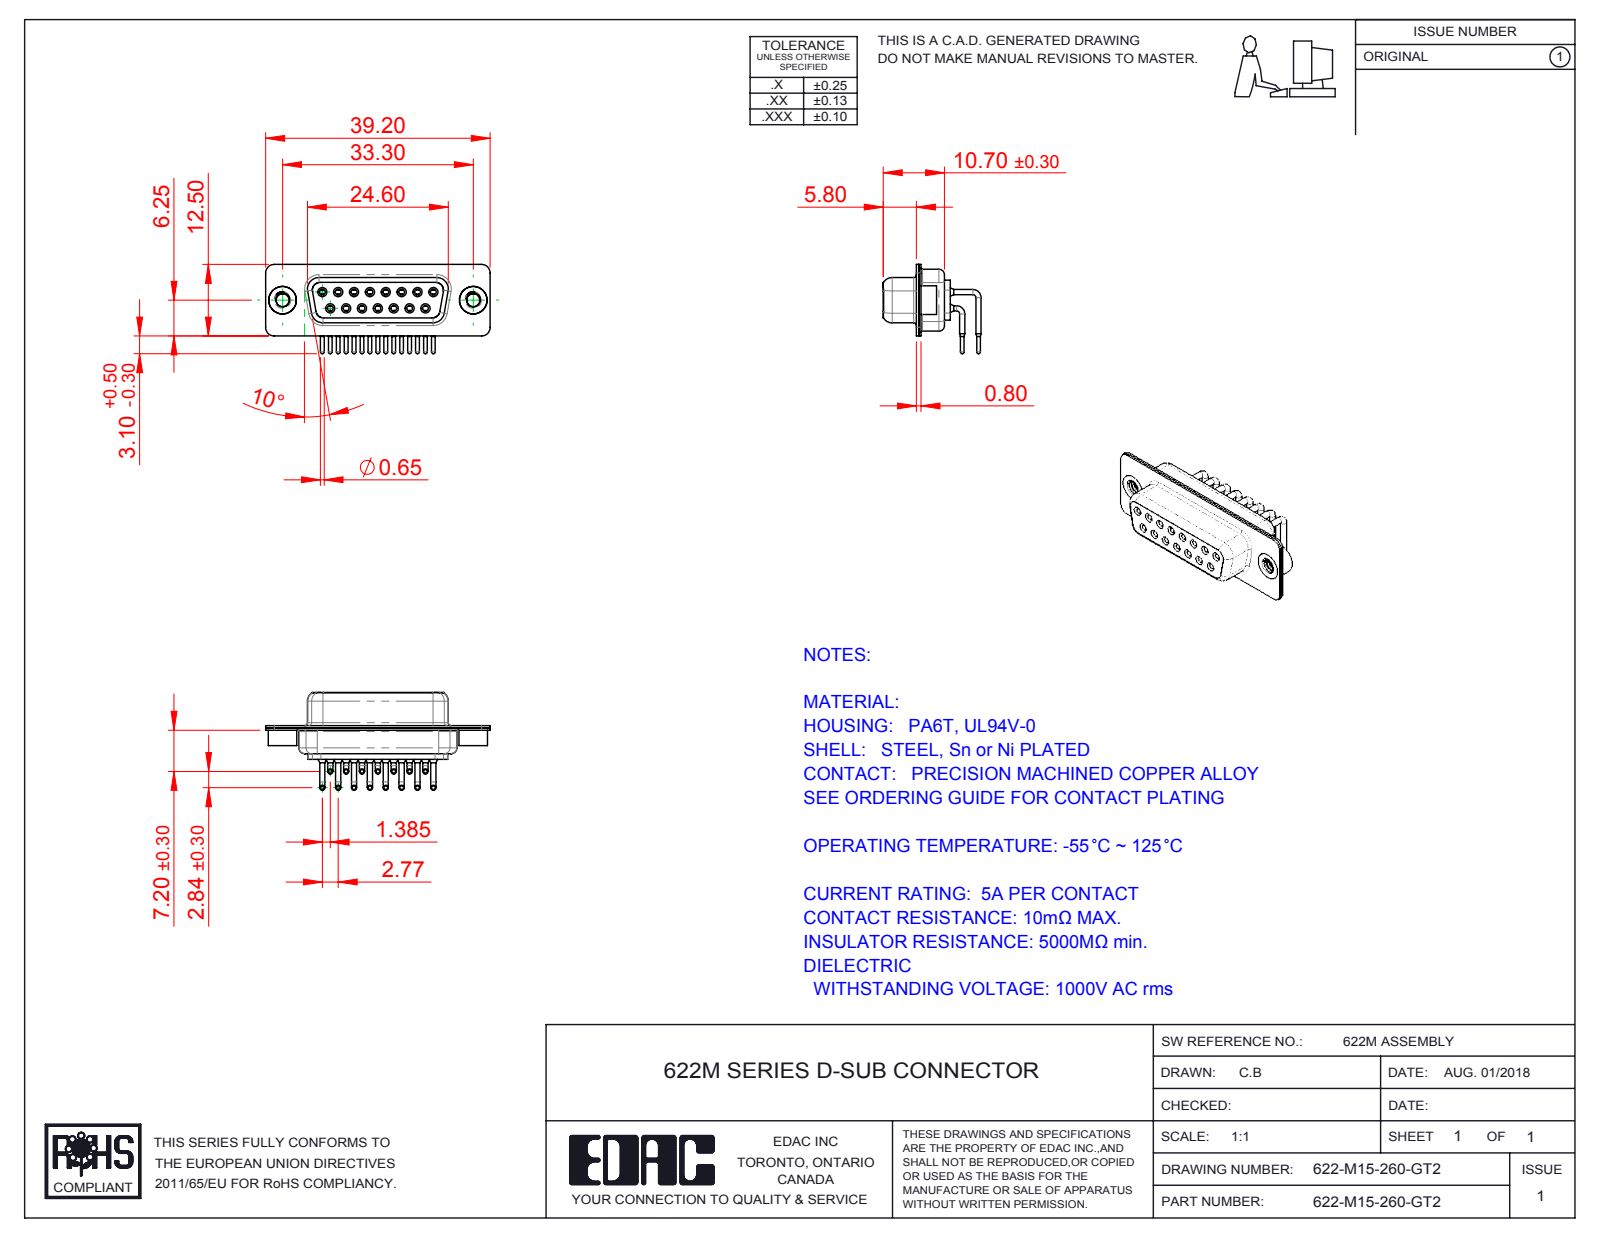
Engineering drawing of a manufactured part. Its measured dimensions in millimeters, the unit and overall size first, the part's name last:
Units: millimetres
Overall size (bounding box): 39.2 × 17.09 × 15.6
Round holes (diameter × count): ⌀1 ×15, ⌀1.1 ×15, ⌀1.7 ×15, ⌀1.8 ×15, ⌀2 ×15, ⌀2.26 ×2, ⌀4 ×2, ⌀4.8 ×2
Round bosses / shafts (diameter × count): ⌀0.9 ×30, ⌀1.6 ×15, ⌀1.5 ×15, ⌀0.65 ×15, ⌀5 ×2, ⌀4.9 ×2
Partial cylindrical surfaces — rounded edges, fillets, slot ends (radius × count): R1.5 ×16, R2 ×12, R1.35 ×8, R1.6 ×8, R0.25 ×4, R0.5 ×4, R0.6 ×4, R0.65 ×4
Main face-to-face distances: 0.4, 1.45, 8.95, 2.3, 6.2, 0.8, 1.9, 8.5, 0.45, 7.05
Hole centre spacings: 3.16, 2.77, 5.54, 8.31, 11.08, 5.03, 5.04, 7.48
Volume: 2 540 mm³ · Surface area: 6 418 mm²
Bodies: 20 solids, 1074 faces (292 planar, 482 cylindrical, 300 other)
Part name (STEP PRODUCT): 622M Shell Front_15 Contacts; 622M Housing_15 Contacts; 622M 4-40 Threaded Rivet; 622M Contact Row 2 (+3 more)
STEP written by: SolidWorks 2016 (CONFIG_CONTROL_DESIGN)
